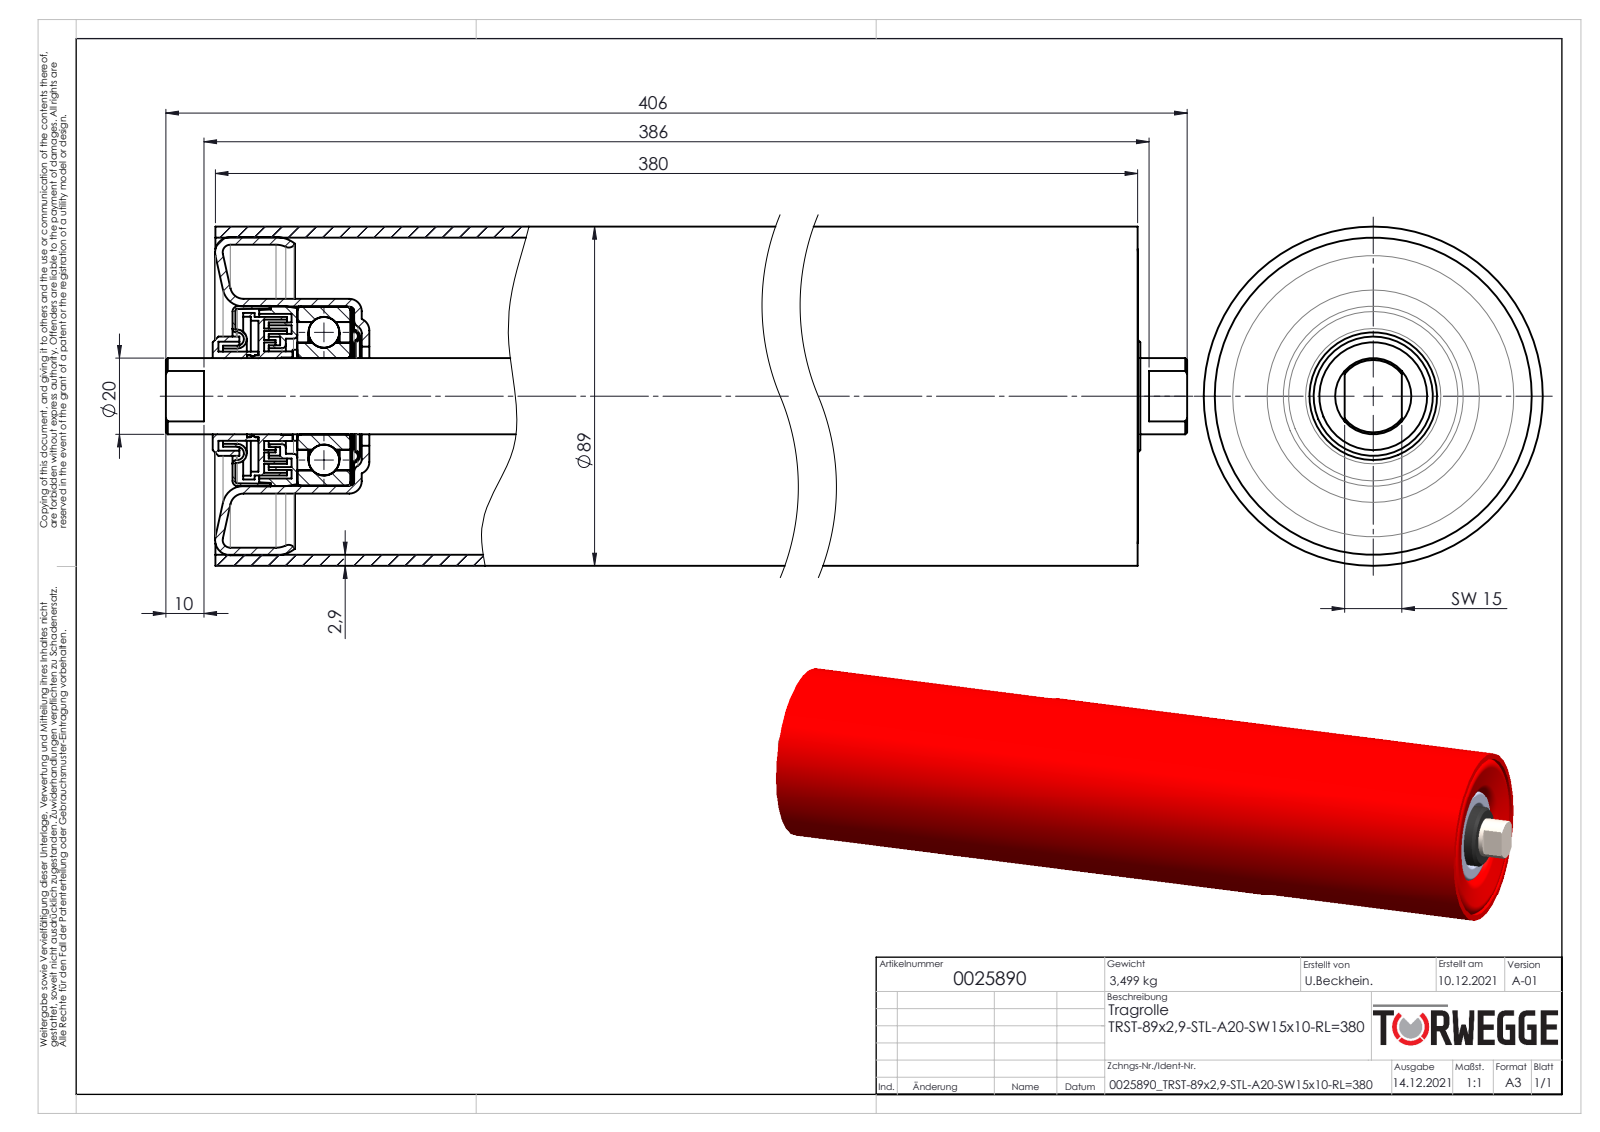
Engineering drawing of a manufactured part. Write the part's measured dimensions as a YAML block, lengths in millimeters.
part_name: "0025890"
step_written_by: "SolidWorks 2020 (AUTOMOTIVE_DESIGN)"
units: millimeters
bodies: {solids: 24, faces: 606, planar: 114, cylindrical: 244, other: 248}
overall_size: [406, 89, 89]
volume: 577466
surface_area: 388024
round_holes:
  - {diameter: 2, count: 4}
  - {diameter: 19, count: 1}
  - {diameter: 19.6, count: 1}
  - {diameter: 20, count: 1}
  - {diameter: 20.3, count: 1}
  - {diameter: 21, count: 1}
  - {diameter: 21.5, count: 1}
  - {diameter: 25, count: 1}
  - {diameter: 25.2, count: 1}
  - {diameter: 26, count: 1}
  - {diameter: 28.2, count: 1}
  - {diameter: 28.6, count: 1}
round_bosses_or_shafts:
  - {diameter: 23.9, count: 2}
  - {diameter: 89, count: 1}
  - {diameter: 83.5, count: 1}
  - {diameter: 51.1, count: 1}
  - {diameter: 47.2, count: 1}
  - {diameter: 47, count: 1}
  - {diameter: 46.5, count: 1}
  - {diameter: 43.7, count: 1}
partial_cylinders:
  - {radius: 2, count: 8}
  - {radius: 13.5, count: 1}
face_to_face_distances: [14, 323.02, 14.92, 322.1, 0.92, 308.1, 337.02, 10.2, 24.2, 25.12]
hole_center_spacings: [11.49, 11.5, 22.55, 3.99, 4, 21.43, 22.99]
